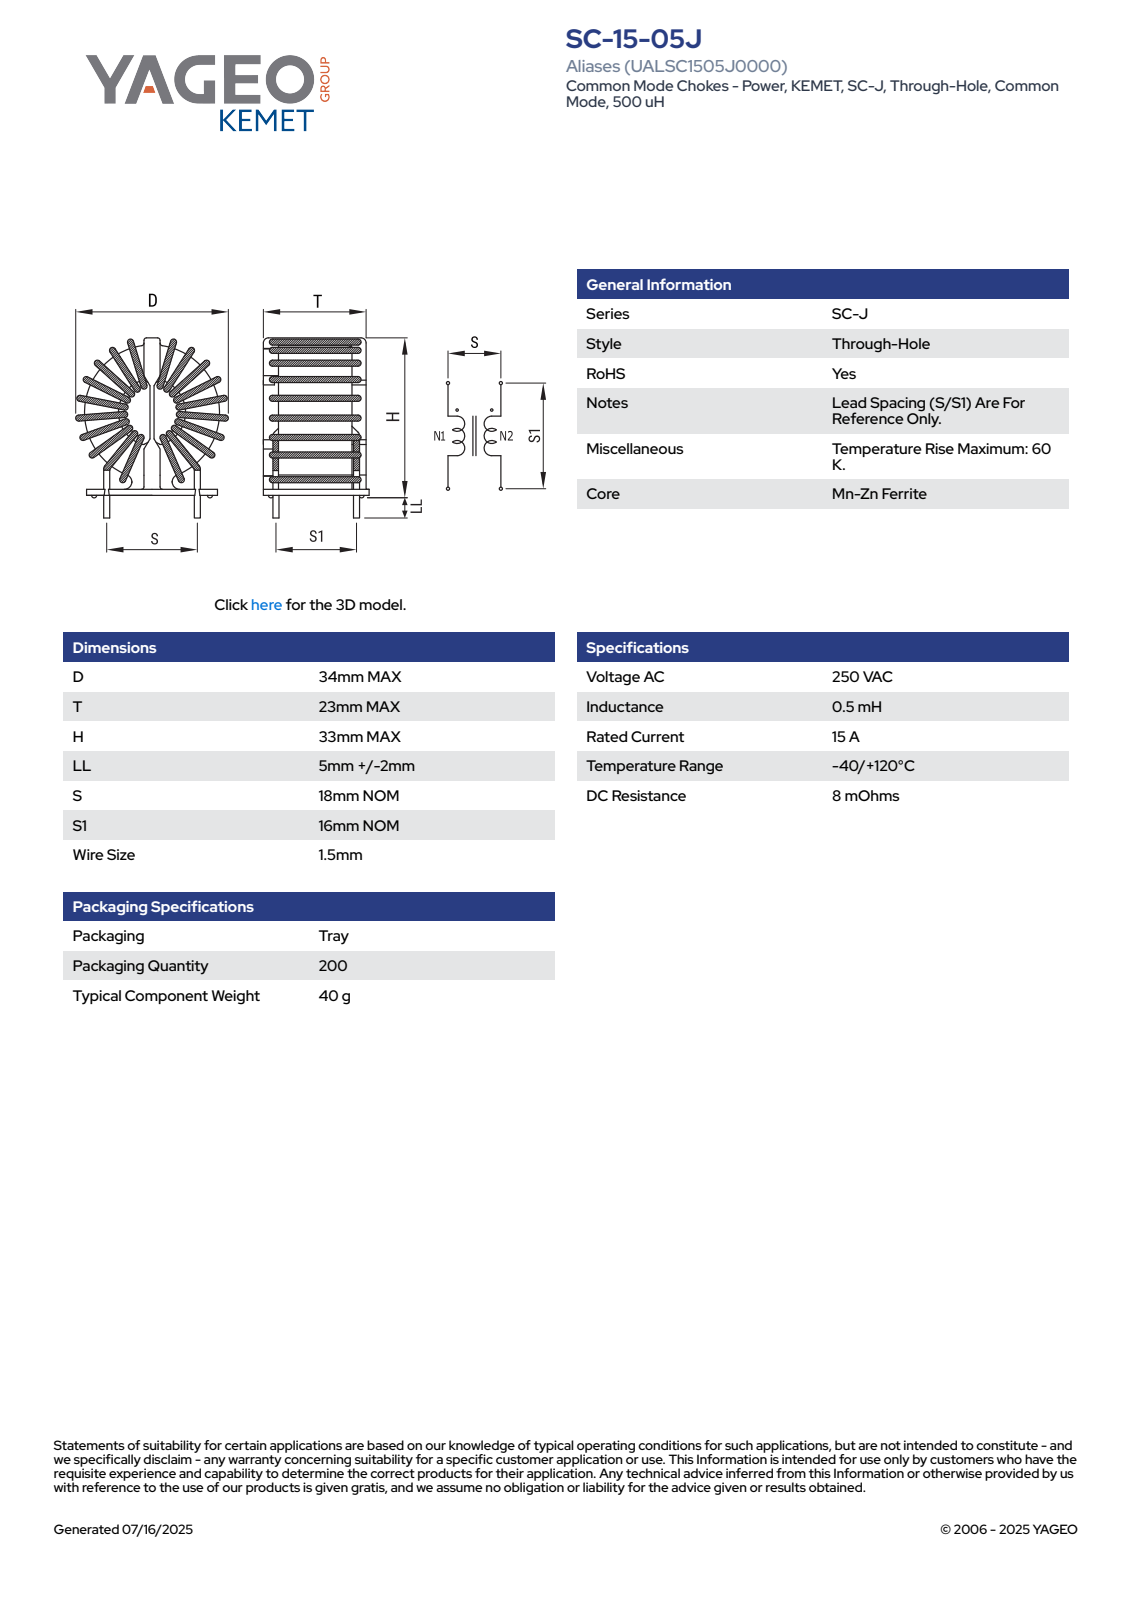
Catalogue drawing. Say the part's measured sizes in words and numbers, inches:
The part is named "SC-15-05J". Its 3-D file was written by "SolidWorks 2018 (AUTOMOTIVE_DESIGN)". It is 1 solid with 373 faces: 169 planar, 120 cylindrical and 84 other. Overall it measures 1.496 by 1.339 by 0.906 inches. Its volume is 0.892 cubic inches and its surface area 12.04 square inches. Round bosses or shafts: 8 of diameter 0.059, 4 of diameter 0.039. Partial cylindrical surfaces (rounded edges, fillets, slot ends): 22 of radius 0.02, 16 of radius 0.03, 6 of radius 0.039, 4 of radius 0.037, 4 of radius 0.059, 1 of radius 0.177, 1 of radius 0.261, 1 of radius 0.289. The main face-to-face distances are 0.047, 0.748, 0.031, 0.079, 0.661, 0.476, 0.087, 0.118, 0.575, 0.15.
